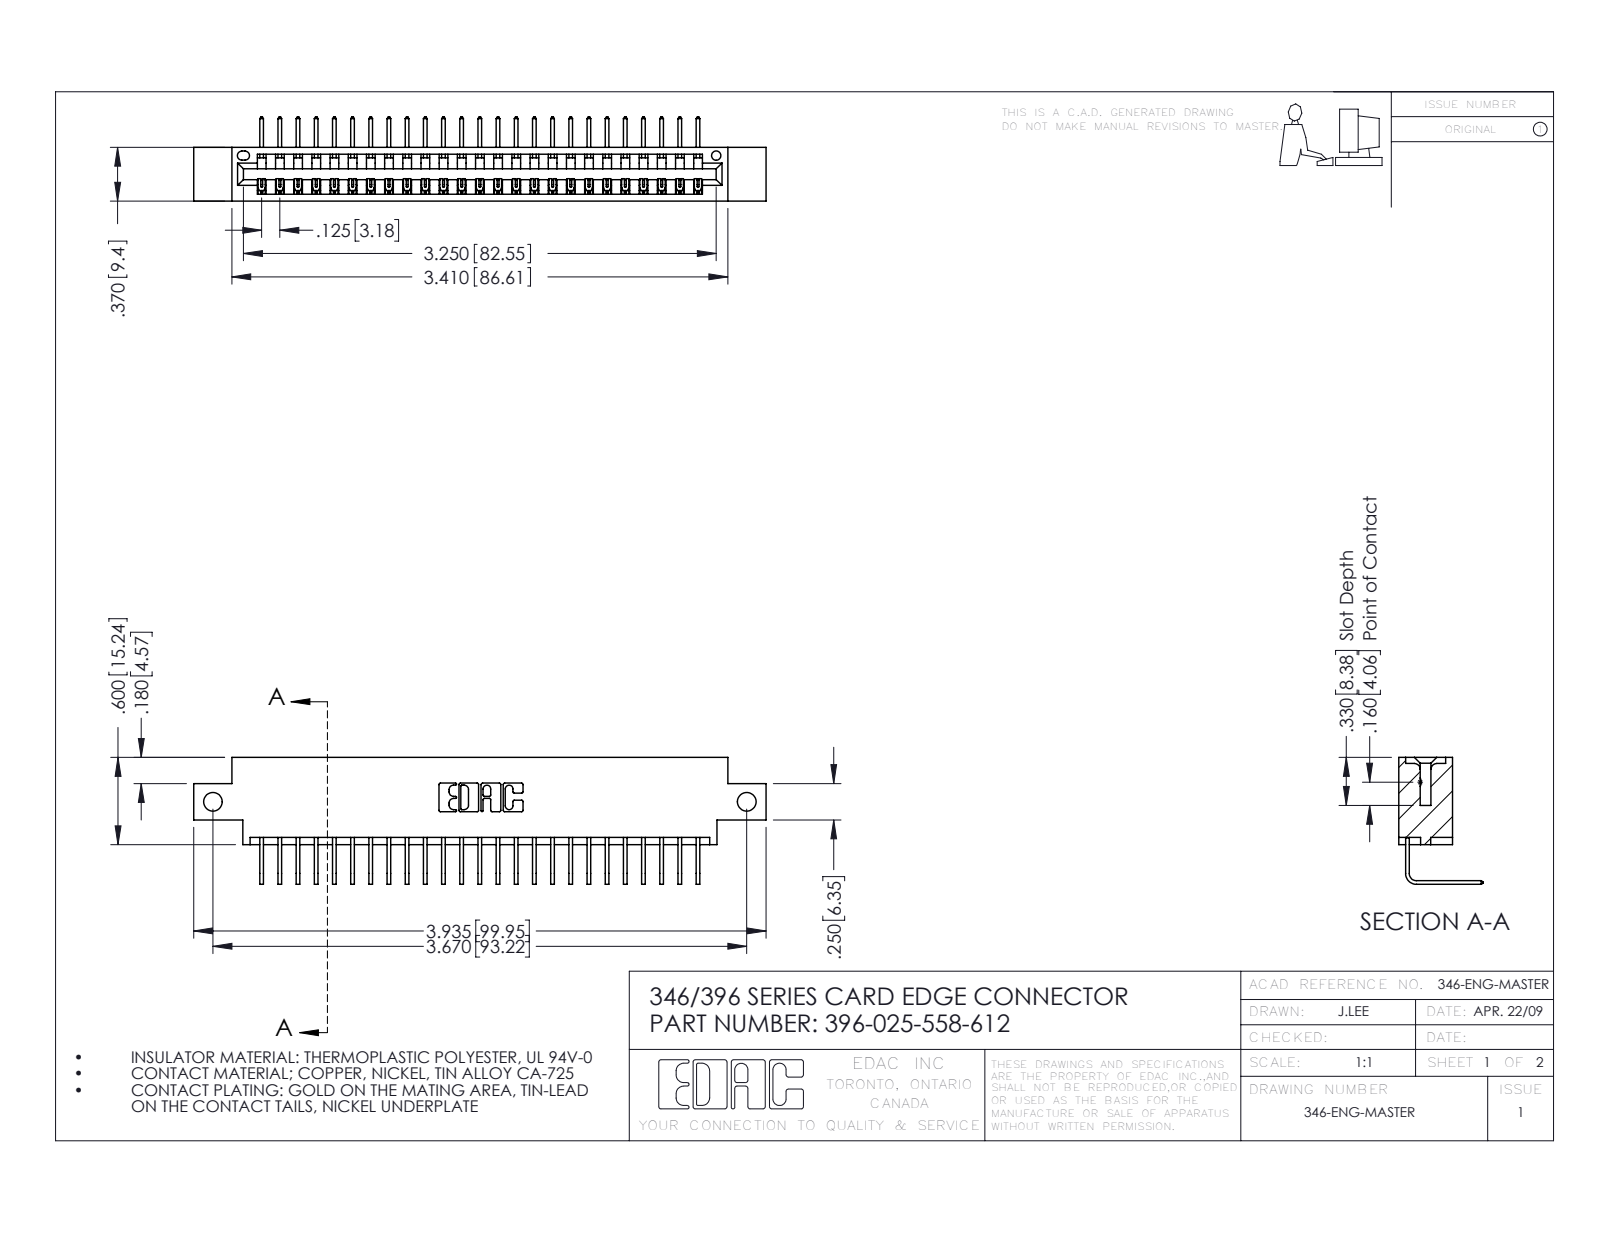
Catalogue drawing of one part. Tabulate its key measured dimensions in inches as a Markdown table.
| quantity | value |
| --- | --- |
| part name | 346 Part_0.170 Offset - Side Mount; 396-025-558-612; 345-292-001_558 Tail - 2 |
| STEP written by | SolidWorks 2016 (CONFIG_CONTROL_DESIGN) |
| units | inches |
| bodies | 26 solids, 1626 faces (1130 planar, 496 cylindrical, 0 other) |
| overall size | 3.935 × 0.873 × 0.58 |
| volume | 0.567 in³ |
| surface area | 18.51 in² |
| round holes (diameter × count) | 0.128 × 2, 0.064 × 1 |
| partial cylindrical surfaces (radius × count) | 0.006 × 50, 0.01 × 22, 0.007 × 6, 0.031 × 6, 0.026 × 3, 0.031 × 2, 0.04 × 2, 0.014 × 1 |
| main face-to-face distances | 0.322, 0.048, 0.37, 0.25, 0.298, 0.025, 0.072, 0.148, 0.222, 0.1 |
| hole center spacings | 3.67 |
